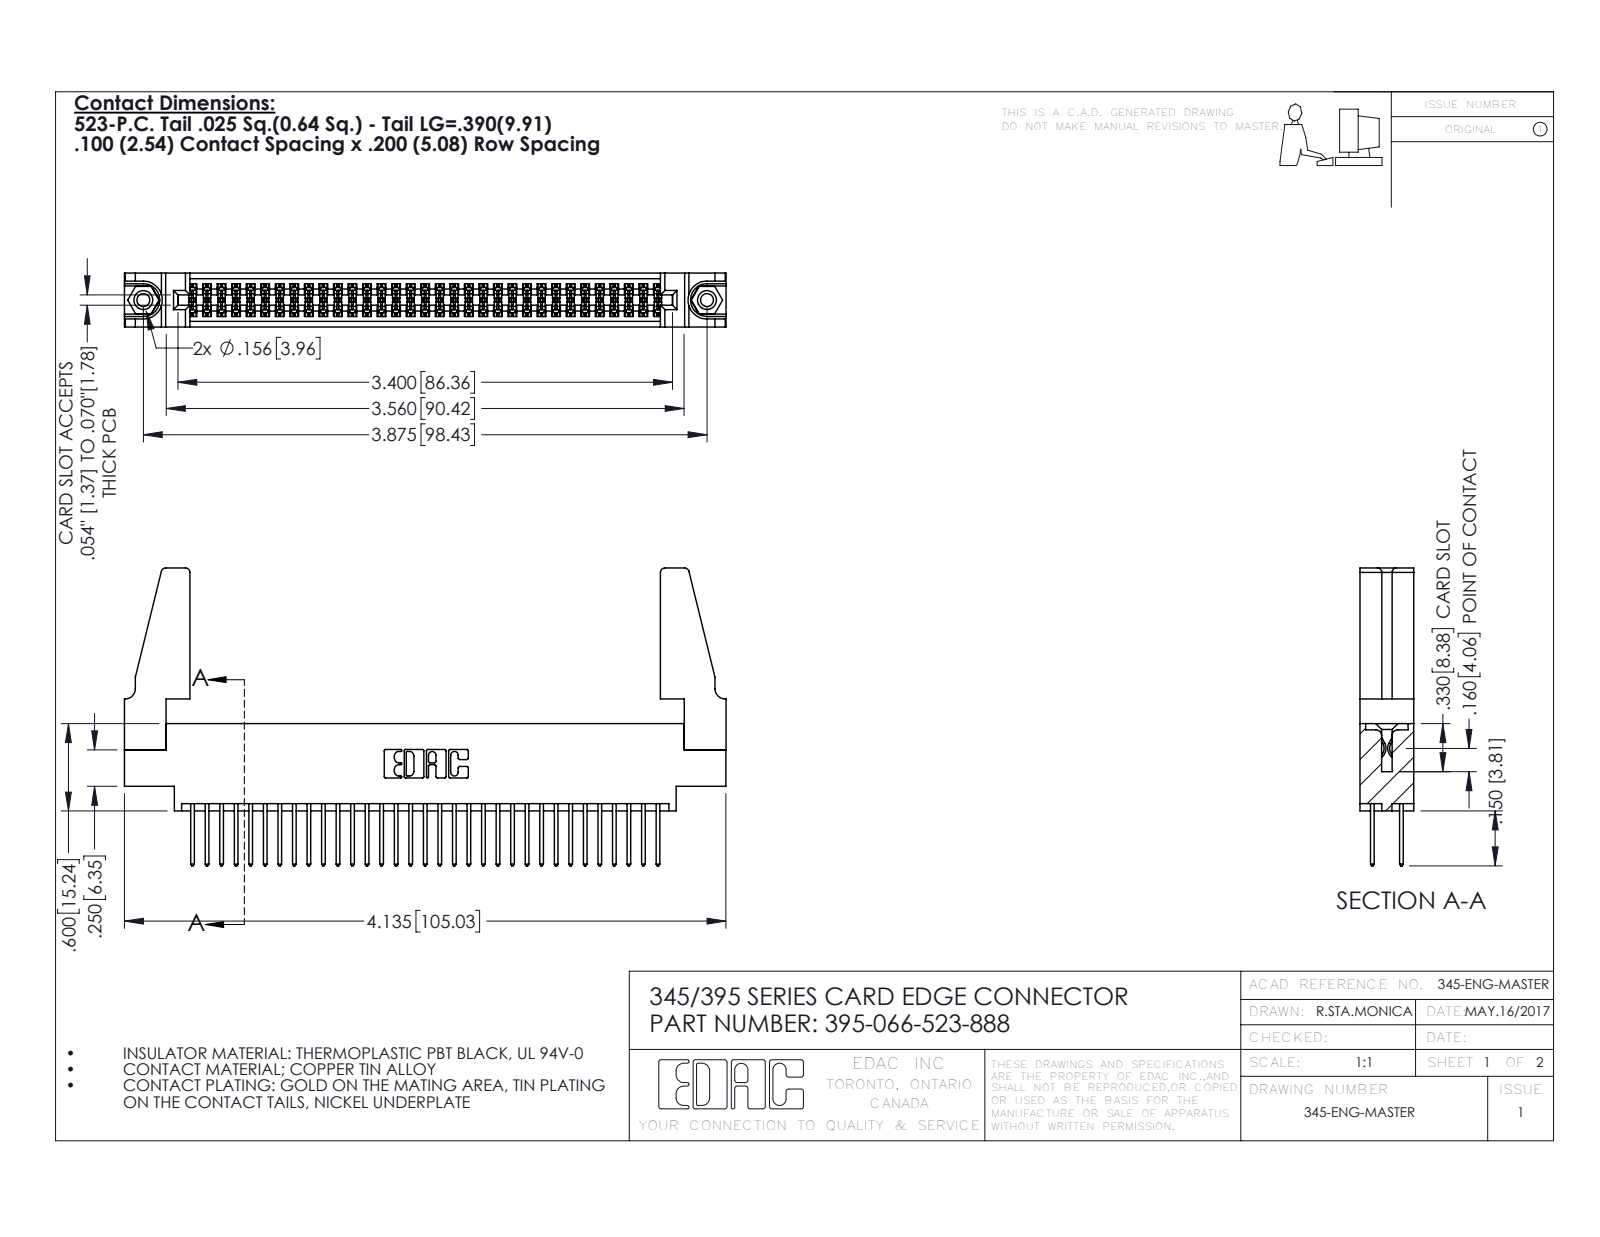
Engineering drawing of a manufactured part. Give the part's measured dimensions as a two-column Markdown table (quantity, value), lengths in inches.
| quantity | value |
| --- | --- |
| part name | 345 Part_0.170 Offset - 0.156 Dia-TH; 345-292-001_345-293-123; 395-066-523-888; 345-220-078_345-220-088 (+1 more) |
| STEP written by | SolidWorks 2016 (CONFIG_CONTROL_DESIGN) |
| units | inches |
| bodies | 71 solids, 3554 faces (2334 planar, 1204 cylindrical, 16 other) |
| overall size | 4.136 × 2.047 × 0.37 |
| volume | 0.817 in³ |
| surface area | 28.97 in² |
| round holes (diameter × count) | 0.089 × 2, 0.125 × 2, 0.156 × 2, 0.064 × 1 |
| round bosses / shafts (diameter × count) | 0.155 × 2 |
| partial cylindrical surfaces (radius × count) | 0.006 × 99, 0.01 × 66, 0.01 × 22, 0.03 × 8, 0.007 × 6, 0.031 × 6, 0.026 × 3, 0.014 × 2 |
| main face-to-face distances | 0.072, 0.298, 0.37, 0.2, 0.098, 0.272, 0.025, 0.225, 0.175, 0.149 |
| hole center spacings | 0.27, 3.64, 3.875 |
